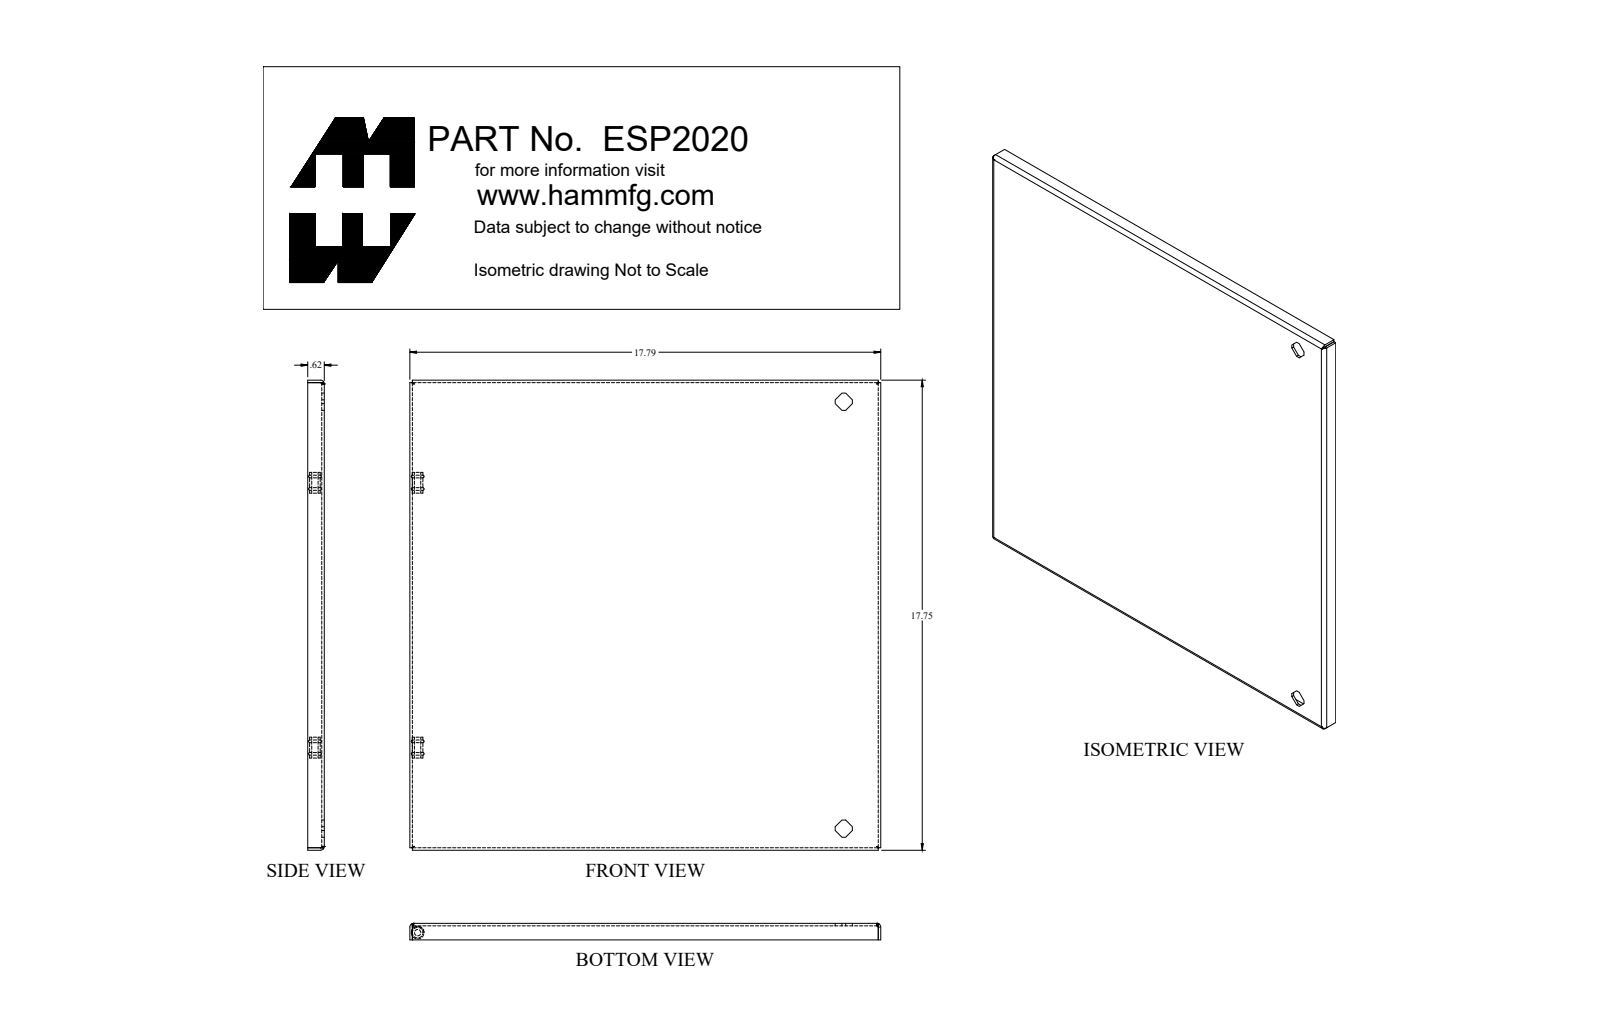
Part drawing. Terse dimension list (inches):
name: ESP2020
written by: SolidWorks 2018 (AUTOMOTIVE_DESIGN)
unit: in
bodies: 13 solids, 584 faces (354 planar, 174 cylindrical, 56 other)
size: 19.708 × 17.752 × 9.953
volume: 46.33 in³; area: 1 175 in²
holes: 2× ⌀0.136, 2× ⌀0.242, 2× ⌀0.516
bosses: 6× ⌀0.232, 2× ⌀0.788, 2× ⌀0.535, 2× ⌀0.496, 2× ⌀0.435, 2× ⌀0.356
rounds: 28× R0.048, 24× R0.01, 6× R0.036, 6× R0.108, 4× R0.06, 4× R0.143, 4× R0.153, 4× R0.156
face distances: 0.095, 0.072, 18.01, 0.775, 0.038, 0.813, 0.038, 16.062, 0.775, 18.082
hole spacings: 10, 16.161
